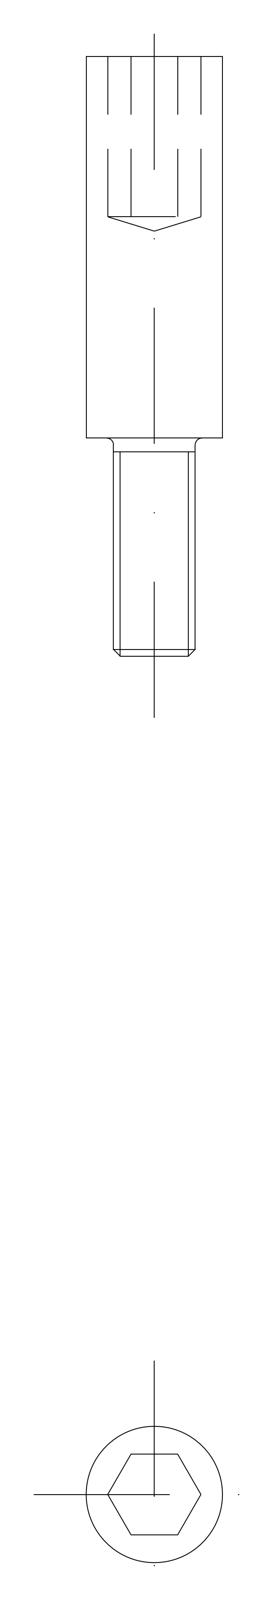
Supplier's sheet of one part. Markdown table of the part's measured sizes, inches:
| quantity | value |
| --- | --- |
| STEP written by | THINKDESIGN (CONFIG_CONTROL_DESIGN) |
| units | inches |
| bodies | 1 solid, 14 faces (10 planar, 2 cylindrical, 2 other) |
| overall size | 1.732 × 0.394 × 0.394 |
| volume | 0.14 in³ |
| surface area | 2.427 in² |
| round bosses / shafts (diameter × count) | 0.394 × 1, 0.236 × 1 |
| main face-to-face distances | 0.233, 0.463, 0.639, 1.102, 0.63, 1.269, 1.732 |
